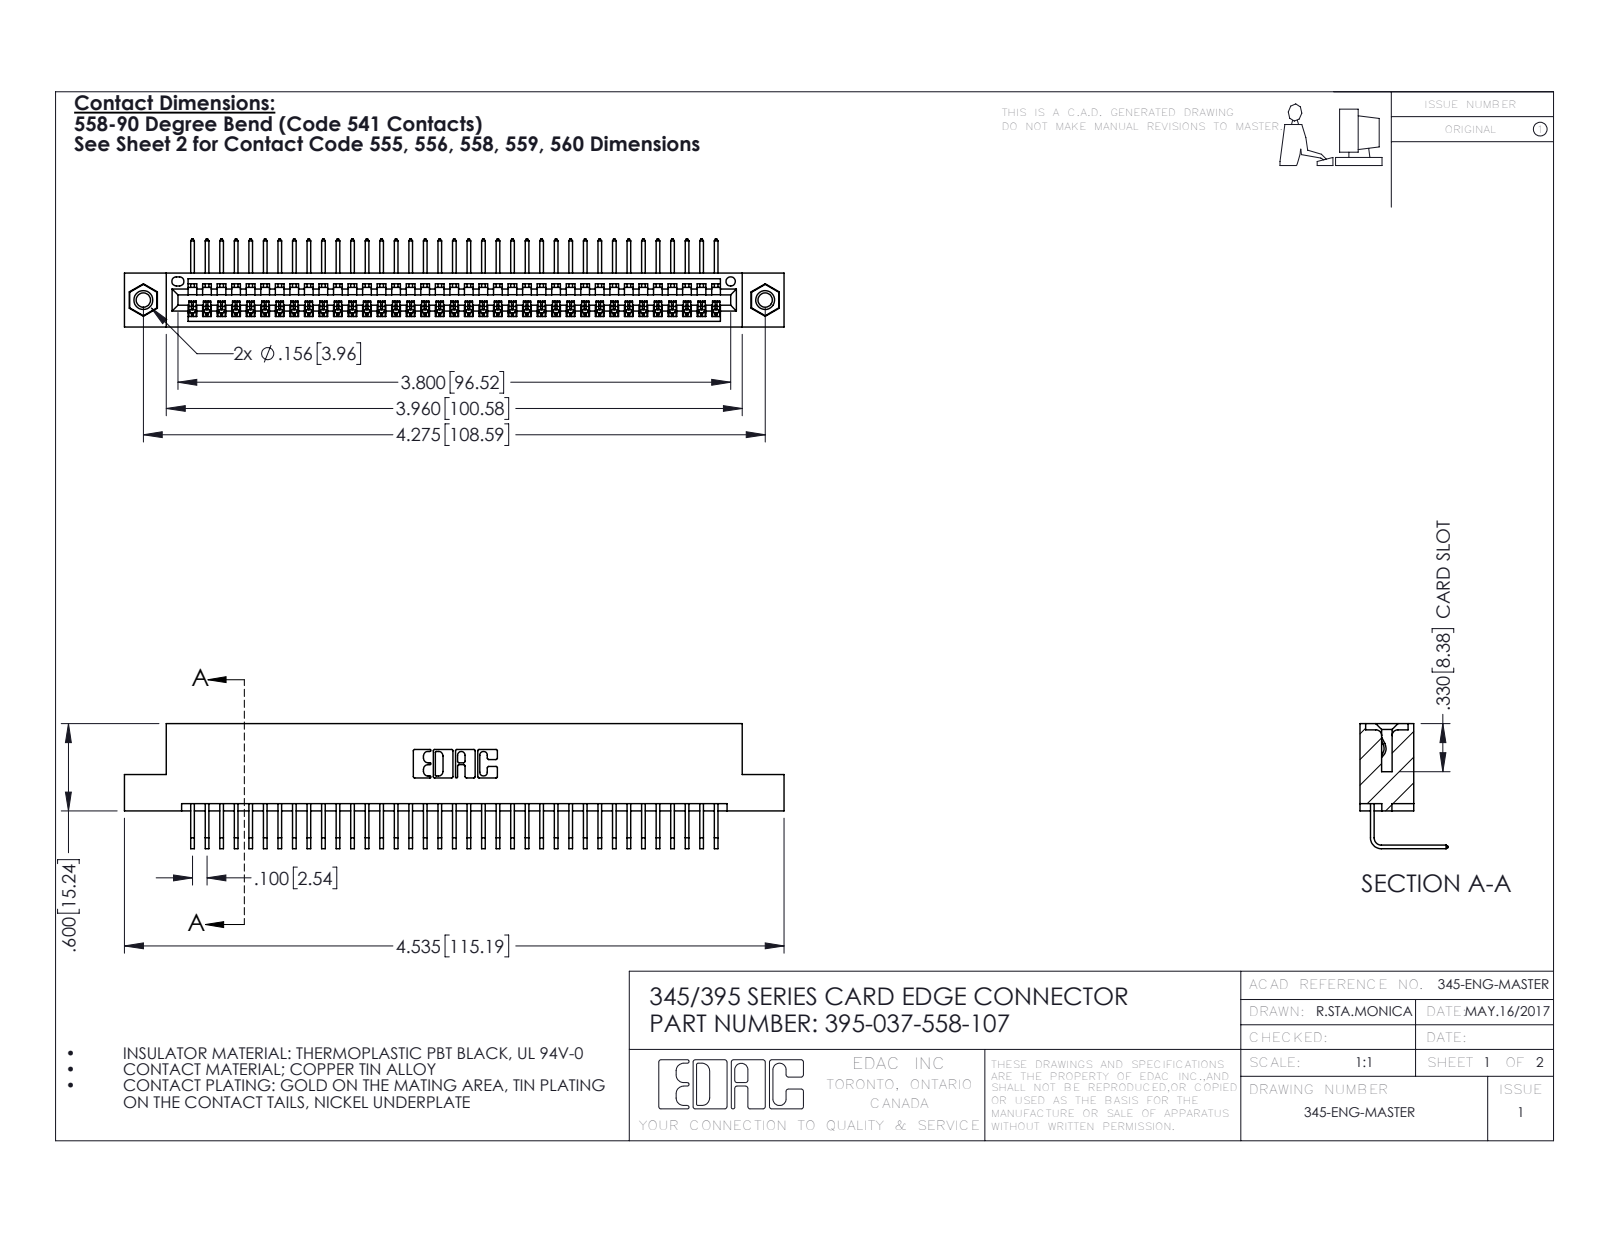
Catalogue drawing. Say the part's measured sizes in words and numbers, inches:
The part is named "345 Part_Flush Mounting Lugs - 0.156 Dia-TI; 345-250-001_345-250-005-103; 395-037-558-107; 345-292-001_558 Tail - 2". Its 3-D file was written by "SolidWorks 2016 (CONFIG_CONTROL_DESIGN)". It is 40 solids with 2406 faces: 1666 planar, 724 cylindrical and 16 other. Overall it measures 4.535 by 0.859 by 0.605 inches. Its volume is 0.672 cubic inches and its surface area 23.75 square inches. Round holes: 2 of diameter 0.098, 2 of diameter 0.125, 2 of diameter 0.156, 1 of diameter 0.064. Round bosses or shafts: 2 of diameter 0.155. Partial cylindrical surfaces (rounded edges, fillets, slot ends): 74 of radius 0.006, 22 of radius 0.01, 6 of radius 0.007, 6 of radius 0.031, 3 of radius 0.026, 2 of radius 0.031, 2 of radius 0.04, 1 of radius 0.014. The main face-to-face distances are 0.072, 0.298, 0.2, 0.37, 0.098, 0.272, 0.025, 0.225, 0.149, 0.072. The hole center spacings are 0.27, 4.039, 4.275.
